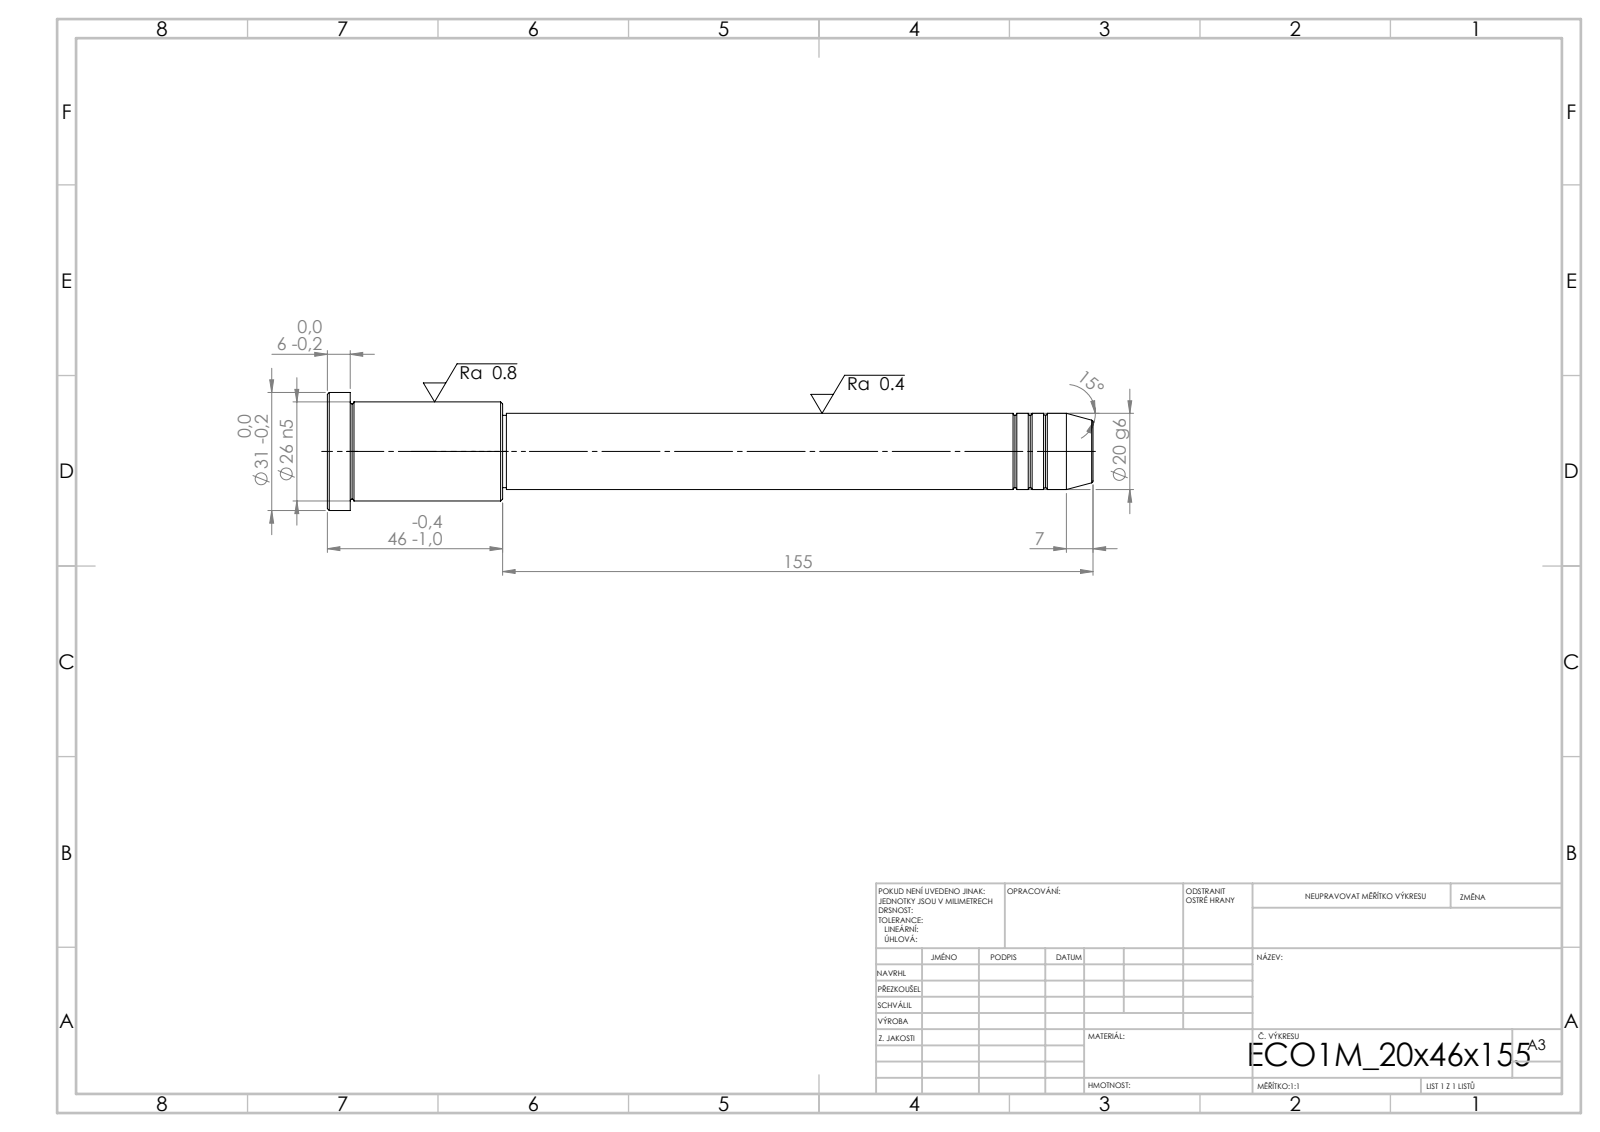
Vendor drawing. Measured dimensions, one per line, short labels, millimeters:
written by: SolidWorks 2019 (CONFIG_CONTROL_DESIGN)
unit: mm
bodies: 1 solid, 43 faces (5 planar, 14 cylindrical, 24 other)
size: 201 × 31 × 31
volume: 73 916 mm³; area: 15 107 mm²
bosses: 1× ⌀31, 1× ⌀26, 1× ⌀20, 1× ⌀19
face distances: 6, 40, 46, 155, 195, 201, 154, 1, 41, 47
